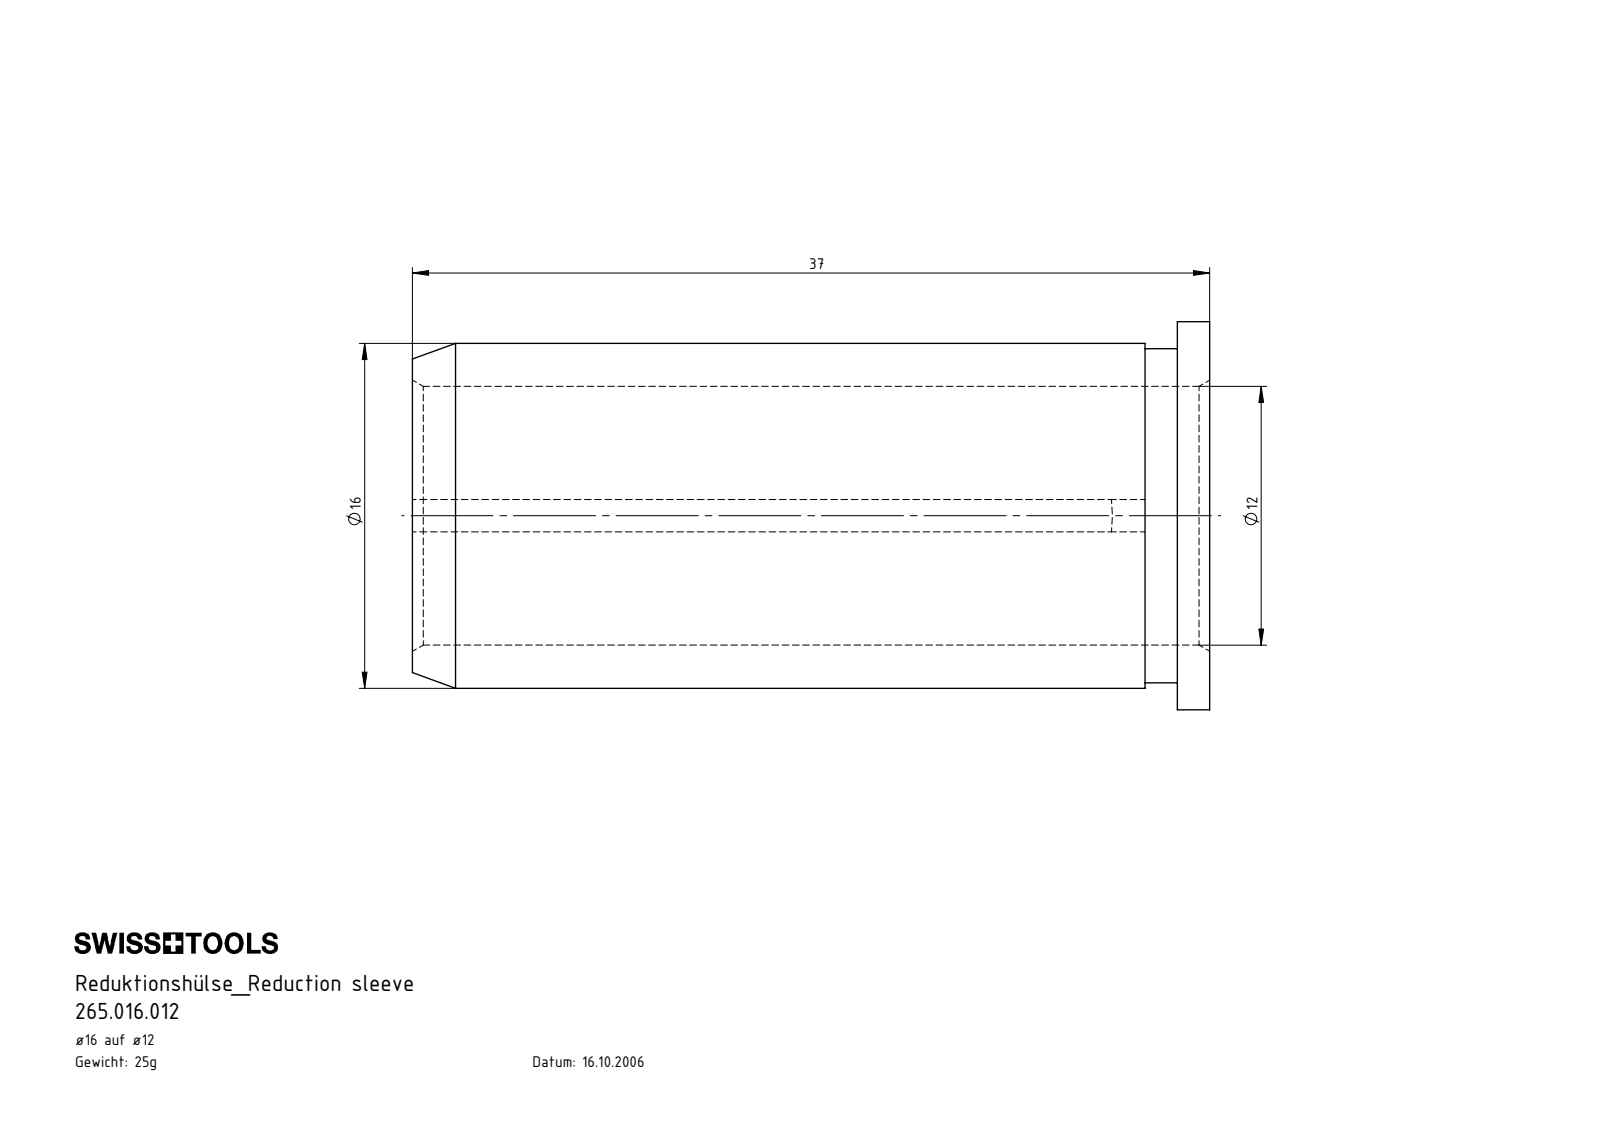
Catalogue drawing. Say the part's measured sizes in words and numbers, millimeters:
The part is named "U12-U16.001.037_A". Its 3-D file was written by "SolidWorks 2012 (CONFIG_CONTROL_DESIGN)". It is 1 solid with 24 faces: 6 planar, 10 cylindrical and 8 other. Overall it measures 37 by 18 by 18 millimeters. Its volume is 3 176 cubic millimeters and its surface area 3 555 square millimeters. Round holes: 1 of diameter 12. Round bosses or shafts: 1 of diameter 18, 1 of diameter 16, 1 of diameter 15.5. Partial cylindrical surfaces (rounded edges, fillets, slot ends): 1 of radius 31.5. The main face-to-face distances are 1.5, 35.5, 37, 34, 3.
